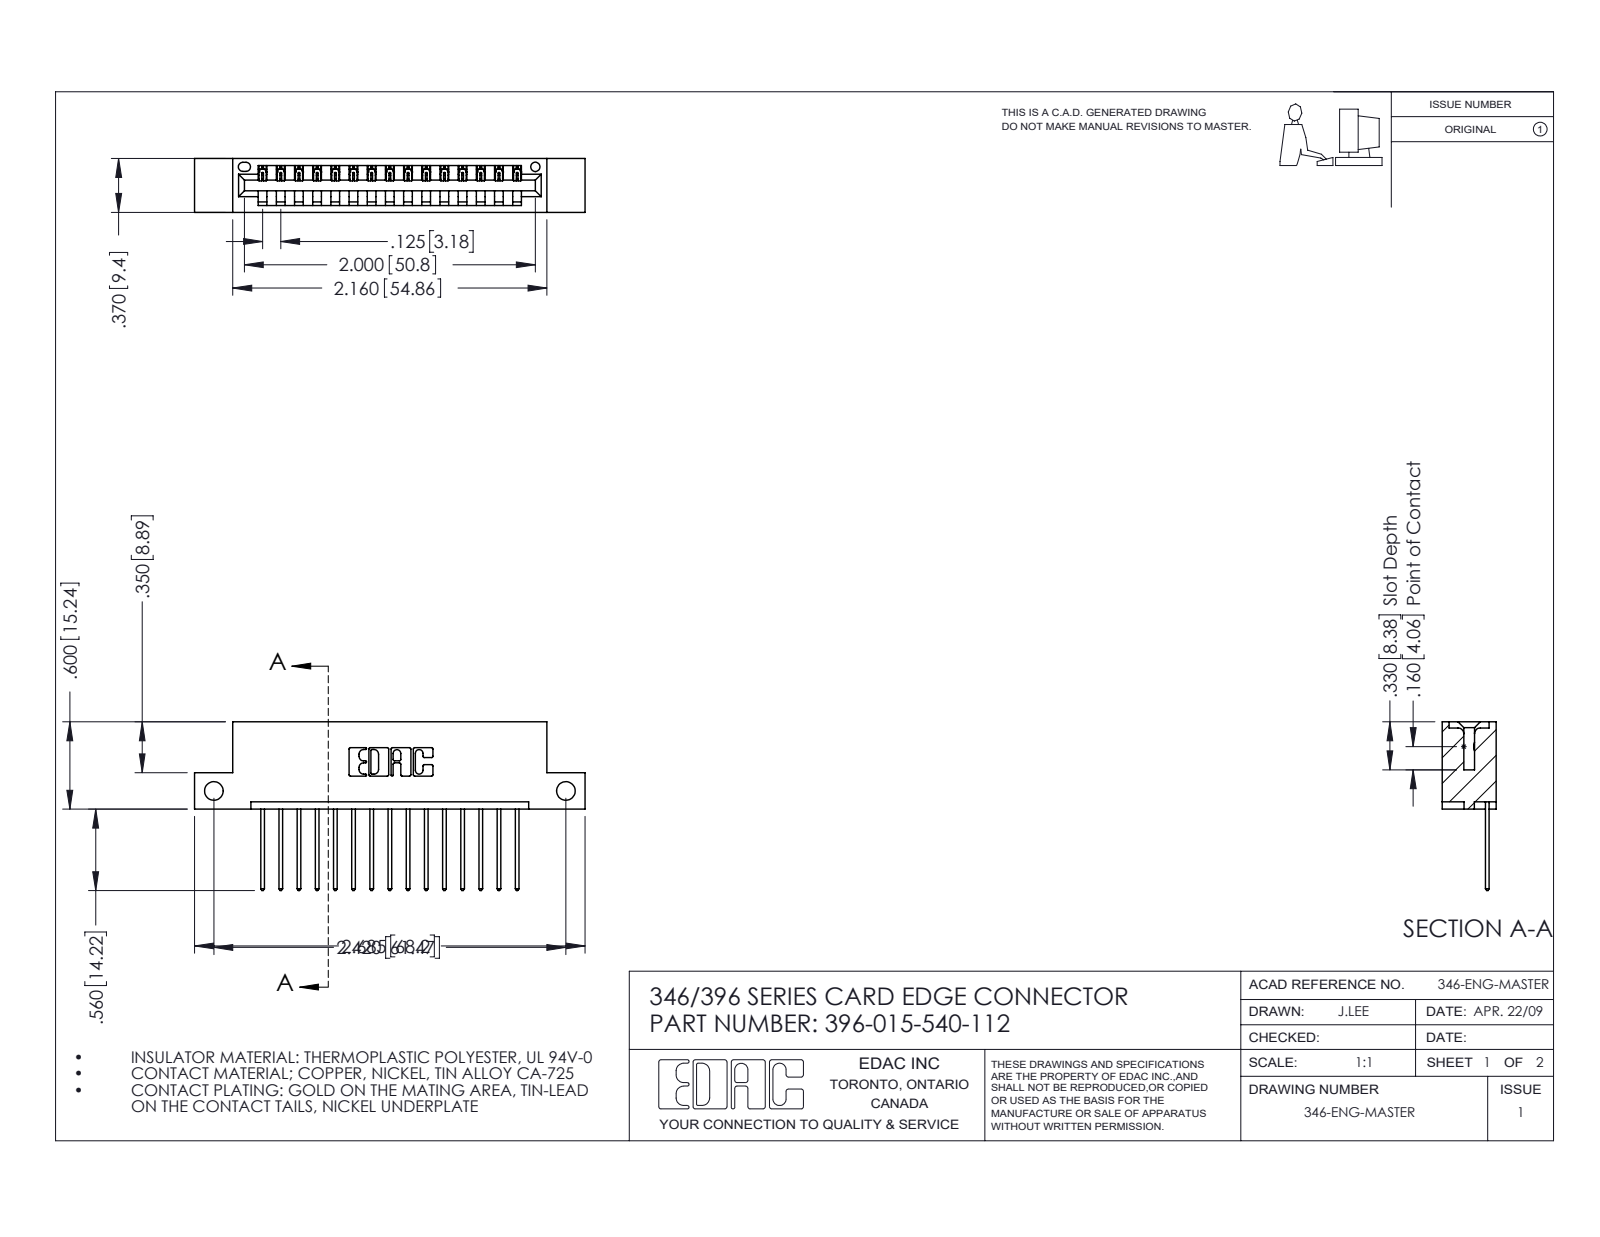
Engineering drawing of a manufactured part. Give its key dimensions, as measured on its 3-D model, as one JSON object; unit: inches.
{"part_name": "346 Part_Flush Mounting Lugs - Side Mount; 345-292-001_345-293-140; 396-015-540-112", "step_written_by": "SolidWorks 2016 (CONFIG_CONTROL_DESIGN)", "units": "inches", "bodies": {"solids": 16, "faces": 992, "planar": 676, "cylindrical": 316, "other": 0}, "overall_size": [2.685, 1.16, 0.37], "volume_in3": 0.383, "surface_area_in2": 11.71, "round_holes": [[0.128, 2], [0.064, 1]], "partial_cylinders_radius": [[0.006, 30], [0.01, 30], [0.01, 22], [0.007, 6], [0.031, 6], [0.026, 3], [0.031, 2], [0.04, 2]], "face_to_face_distances": [0.25, 0.048, 0.322, 0.37, 0.072, 0.298, 0.025, 0.148, 0.222, 0.1], "hole_center_spacings": [2.42]}
